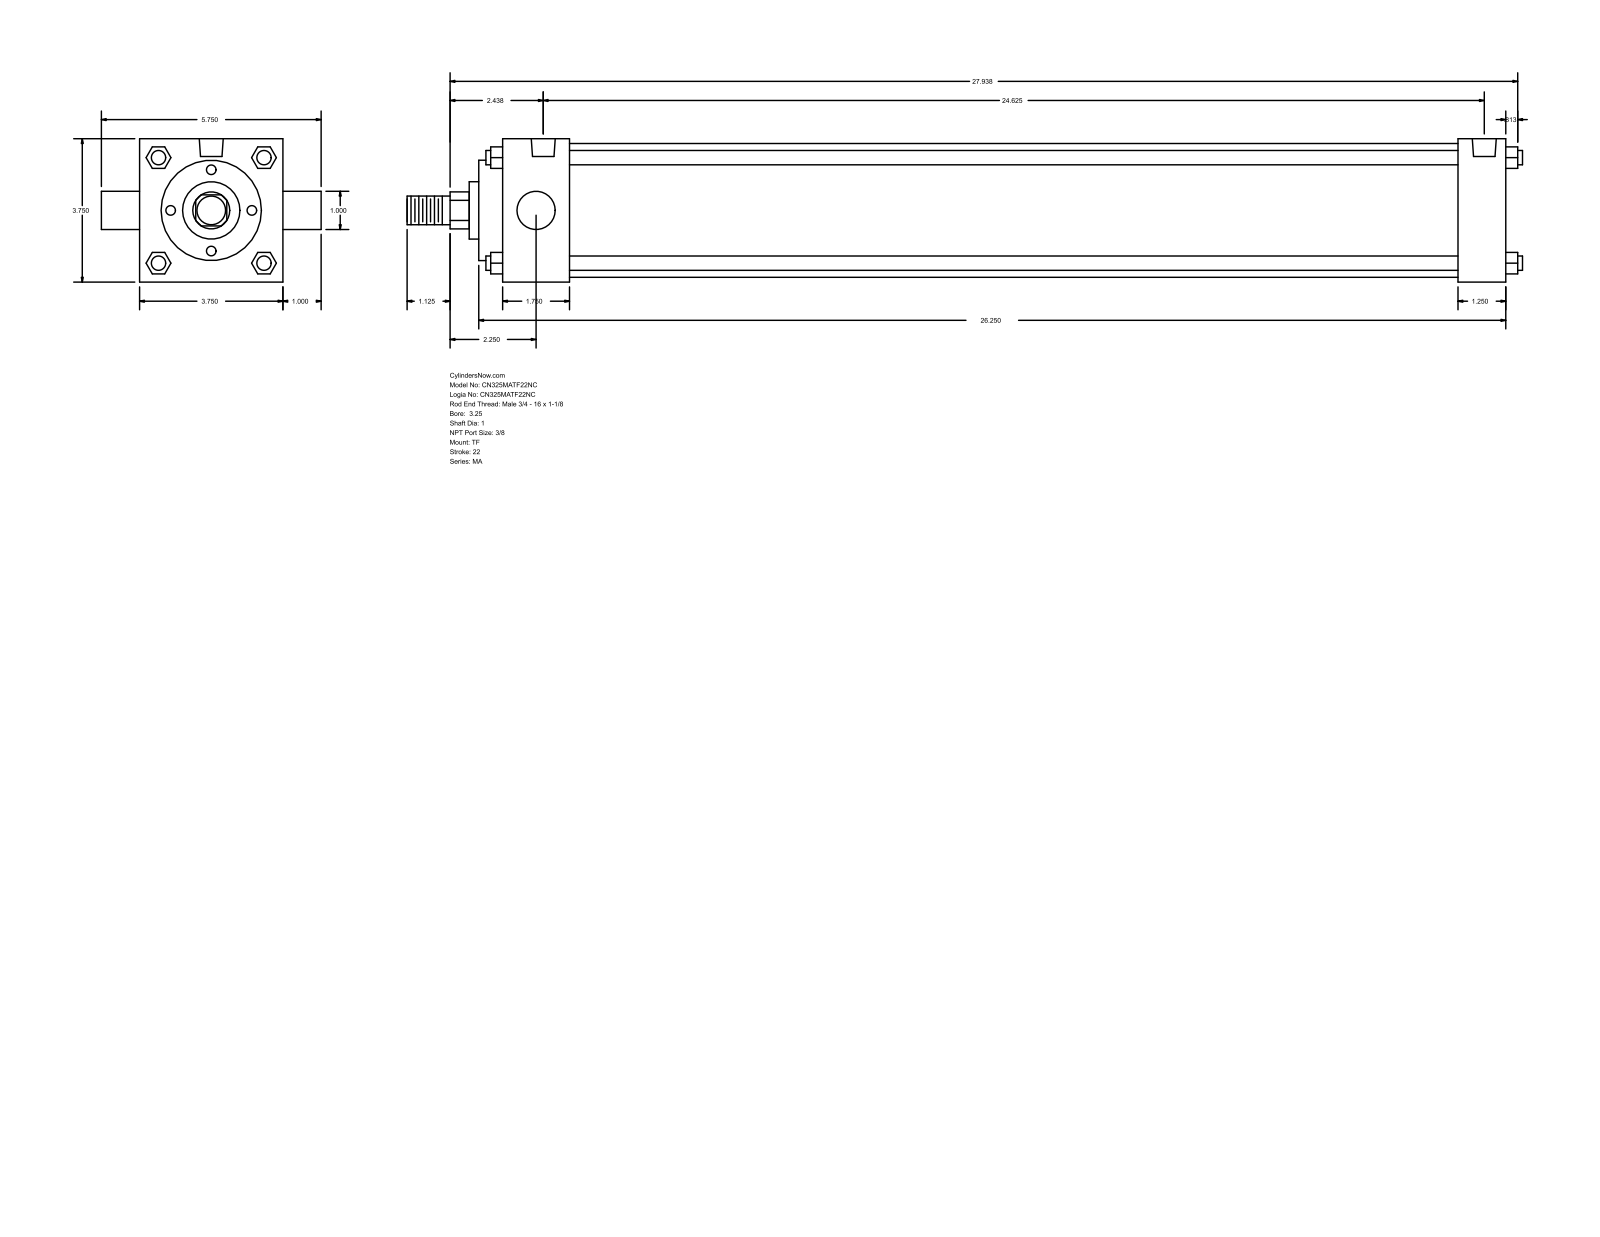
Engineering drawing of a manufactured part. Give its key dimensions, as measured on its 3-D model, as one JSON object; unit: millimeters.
{"part_name": "MA_TF__0325_1", "step_written_by": "GSSL Pune (CONFIG_CONTROL_DESIGN)", "units": "millimeters", "bodies": {"solids": 0, "faces": 122, "planar": 93, "cylindrical": 29, "other": 0}, "overall_size": [741.36, 146.05, 95.25], "round_holes": [[11.11, 3], [15.93, 2]], "round_bosses_or_shafts": [[9.53, 4], [25.4, 2], [88.9, 1], [66.67, 1], [38.1, 1], [19.05, 1]], "partial_cylinders_radius": [[12.29, 1]], "face_to_face_distances": [95.24, 666.75, 682.62, 44.46, 635, 590.54, 622.29, 31.75, 15.87, 60.33], "hole_center_spacings": [4.76, 4.77, 615.95, 620.71, 620.72, 625.48]}
